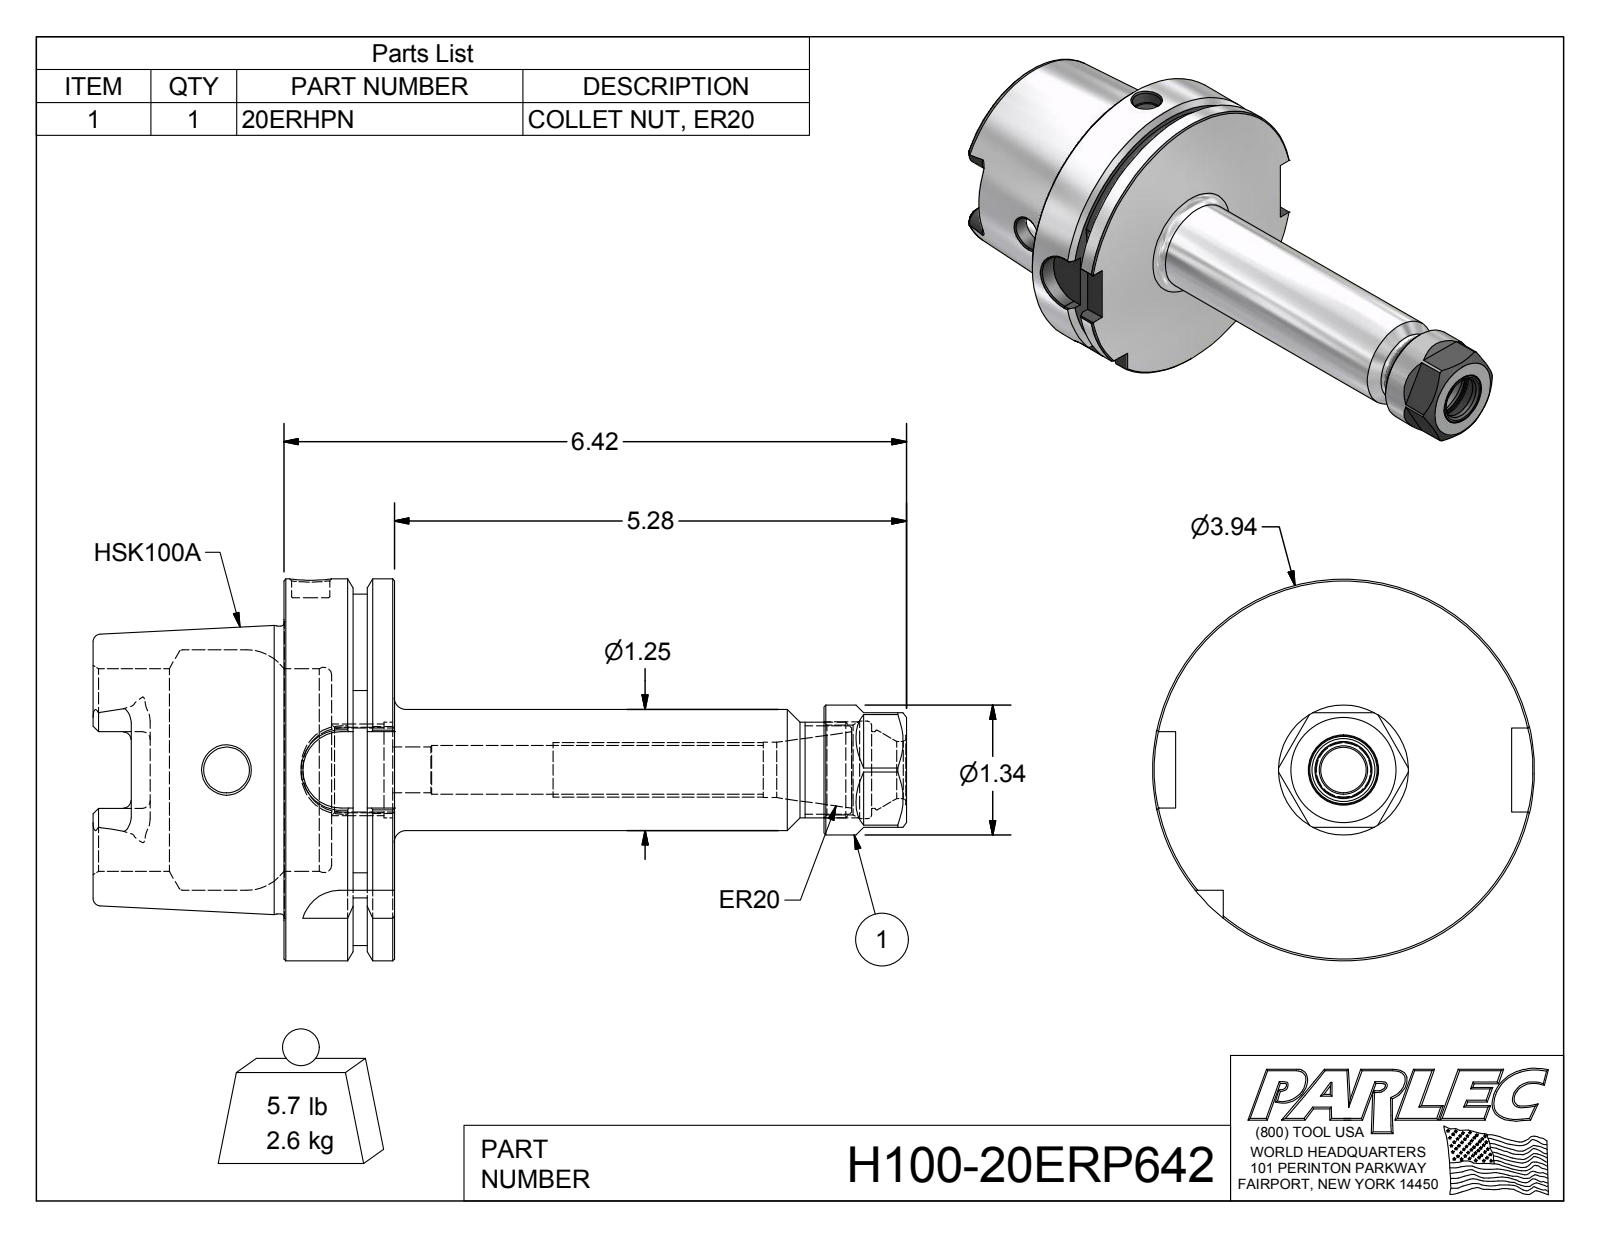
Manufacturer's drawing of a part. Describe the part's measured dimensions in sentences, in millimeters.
The part is named "H100-20ERP642; H100-20ER6-1; 20ERHPN". Its 3-D file was written by "Autodesk Inventor 2012 (AUTOMOTIVE_DESIGN)". It is 2 solids with 163 faces: 60 planar, 41 cylindrical and 62 other. Overall it measures 213.1 by 100 by 100 millimeters. Its volume is 336 600 cubic millimeters and its surface area 70 900 square millimeters. Round holes: 2 of diameter 12, 1 of diameter 10, 1 of diameter 12, 1 of diameter 12.8, 1 of diameter 14.5, 1 of diameter 14.9, 1 of diameter 20.1, 1 of diameter 22.4, 1 of diameter 23.5, 1 of diameter 25, 1 of diameter 25.5, 1 of diameter 53. Round bosses or shafts: 1 of diameter 100, 1 of diameter 75.4, 1 of diameter 34, 1 of diameter 31.8, 1 of diameter 25. Partial cylindrical surfaces (rounded edges, fillets, slot ends): 6 of radius 2, 4 of radius 4.9, 4 of radius 10, 1 of radius 46. The main face-to-face distances are 29, 12.5, 16.5, 50, 62.5, 79, 71.9, 21.9, 9.4, 7.1.
